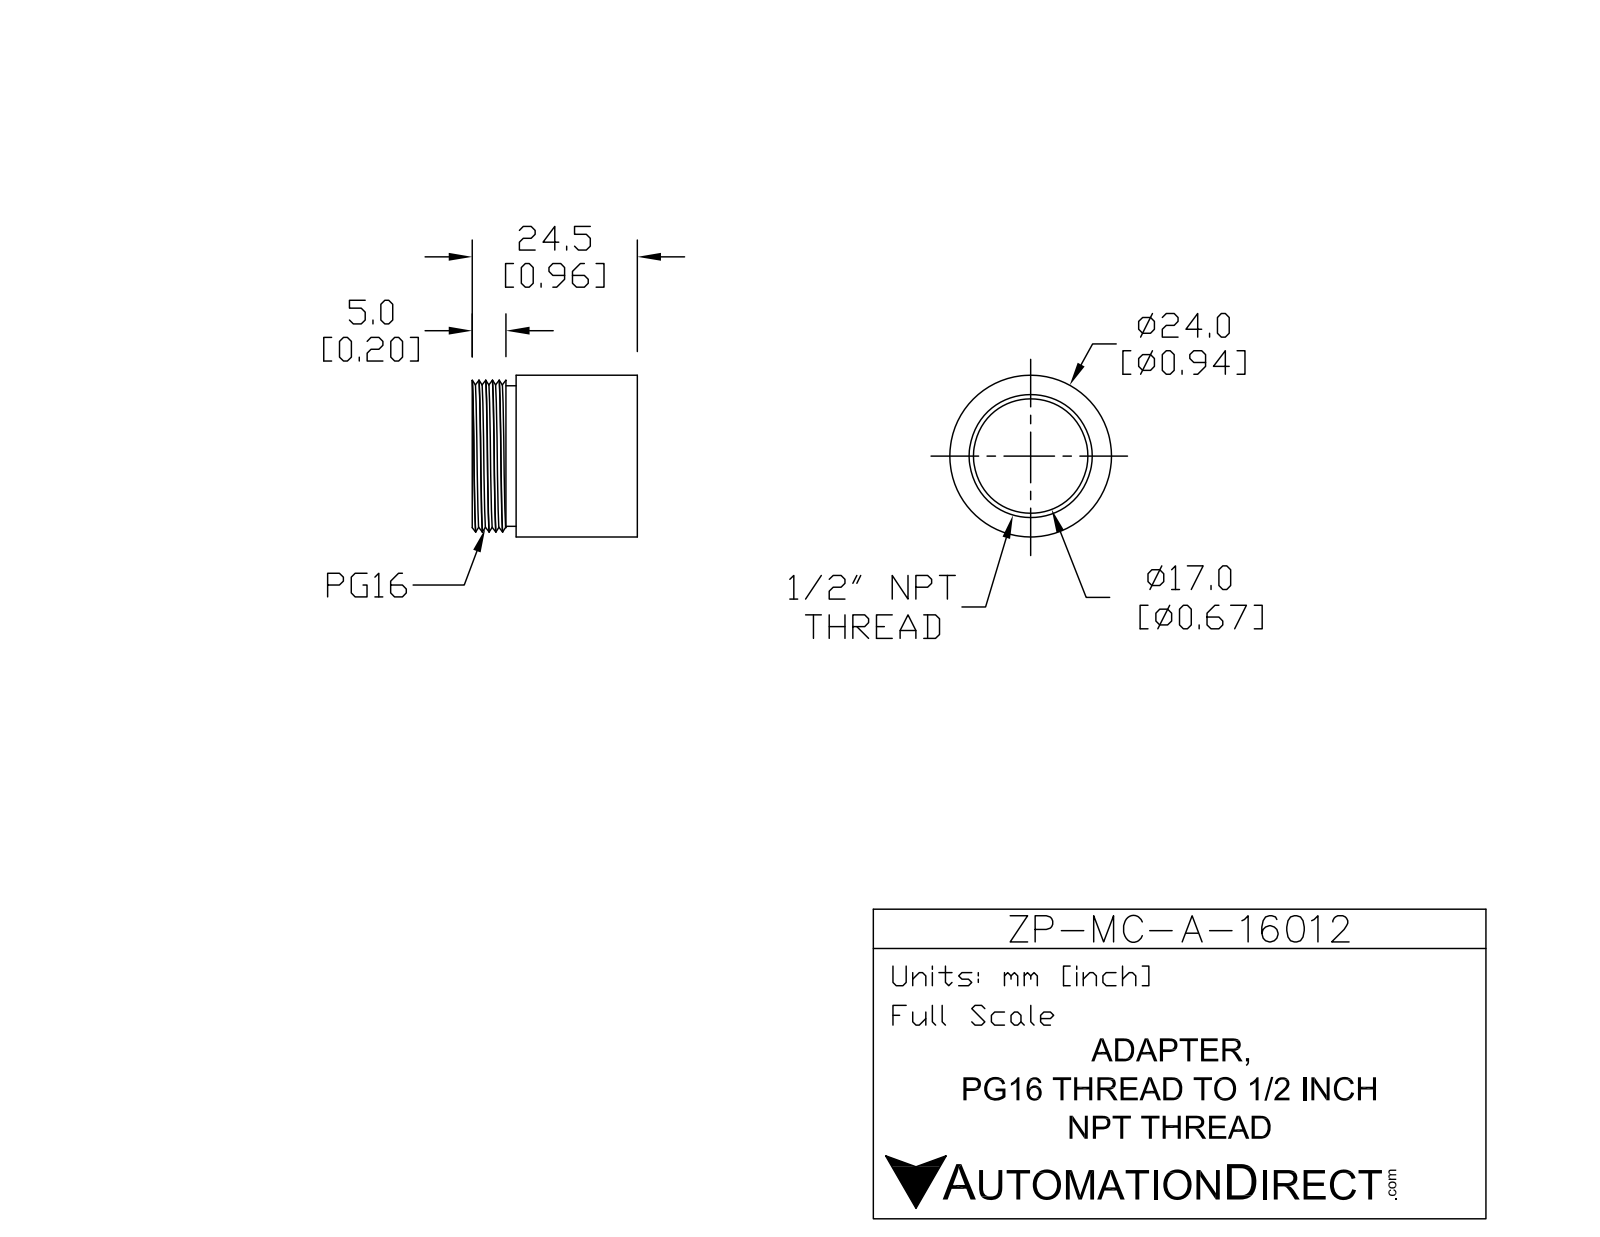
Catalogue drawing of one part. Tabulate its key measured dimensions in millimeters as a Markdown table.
| quantity | value |
| --- | --- |
| part name | ZP-MC-A-16012 |
| STEP written by | SolidWorks 2011 (AUTOMOTIVE_DESIGN) |
| units | millimeters |
| bodies | 1 solid, 29 faces (6 planar, 19 cylindrical, 4 other) |
| overall size | 24.5 × 24 × 24 |
| volume | 4 191 mm³ |
| surface area | 5 083 mm² |
| round holes (diameter × count) | 17 × 1, 18 × 1 |
| round bosses / shafts (diameter × count) | 24 × 1, 22.5 × 1, 20.85 × 1 |
| main face-to-face distances | 24.5, 6.5, 18, 5, 1.5, 19.5, 9.5, 4.5, 3, 15 |
